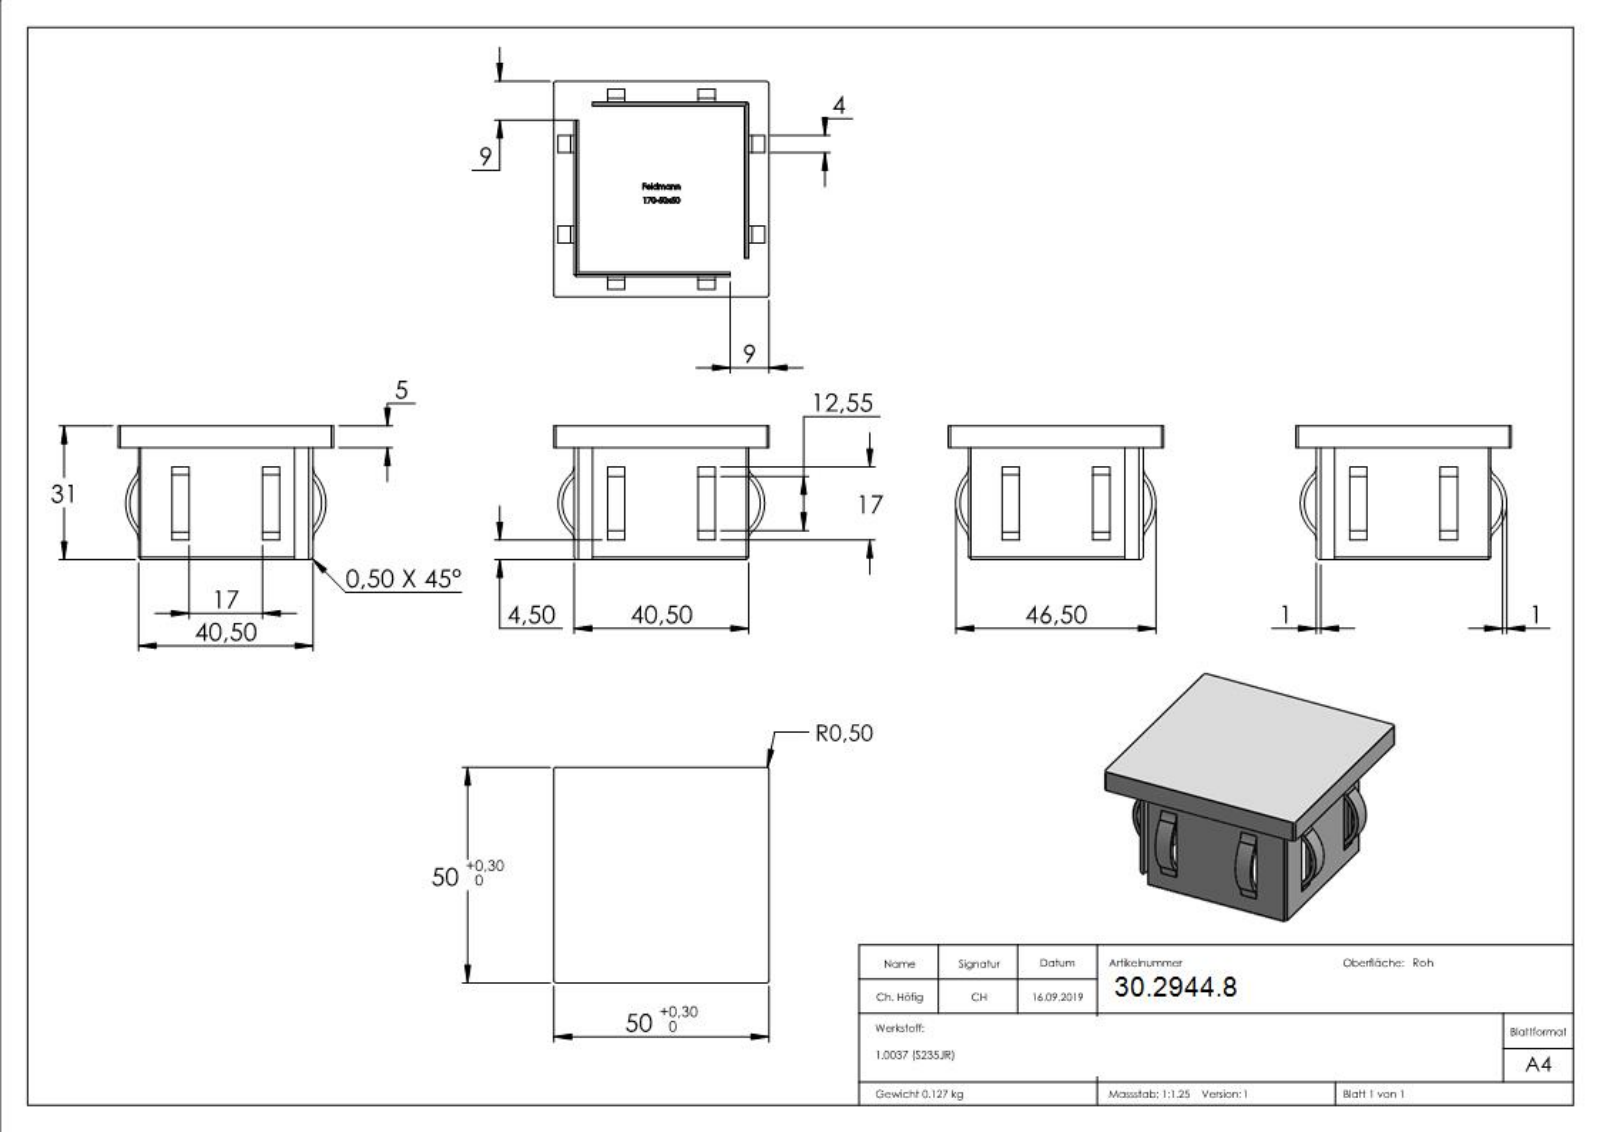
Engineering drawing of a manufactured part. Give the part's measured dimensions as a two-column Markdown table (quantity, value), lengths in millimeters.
| quantity | value |
| --- | --- |
| part name | 170-50x50 |
| STEP written by | SolidWorks 2015 (CONFIG_CONTROL_DESIGN) |
| units | millimeters |
| bodies | 1 solid, 463 faces (264 planar, 62 cylindrical, 137 other) |
| overall size | 50 × 50 × 31 |
| volume | 16 251 mm³ |
| surface area | 14 064 mm² |
| partial cylindrical surfaces (radius × count) | 0.5 × 6, 2.51 × 4, 3.51 × 4, 3.54 × 4, 4.54 × 4, 9 × 4, 8 × 2, 10 × 2 |
| main face-to-face distances | 1, 39.5, 5, 38.5, 40.5, 4.75, 5.75, 44.25, 45.25, 50 |
